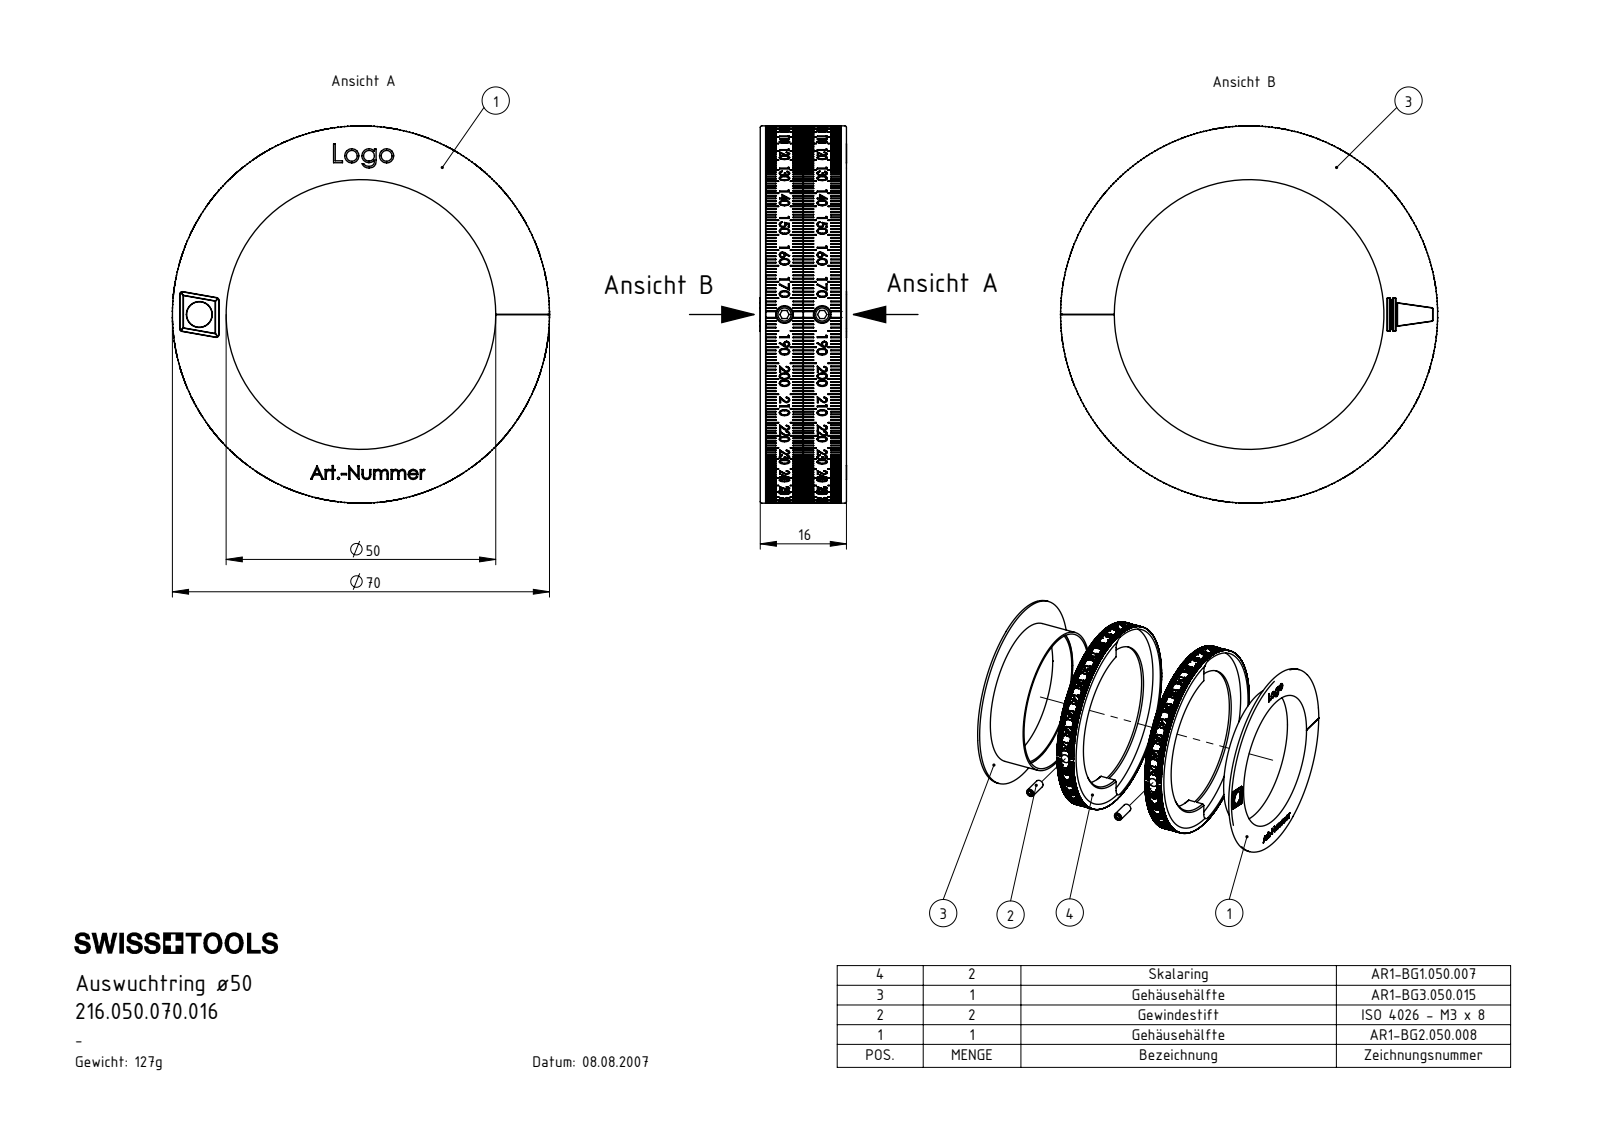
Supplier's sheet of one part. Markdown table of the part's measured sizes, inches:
| quantity | value |
| --- | --- |
| part name | AR1.U50.001.016; AR1-BG3.050.015_A_vereinfachte ansicht; AR1-BG1.050.007_A_vereinfachte ansicht; ISO 4026 - M4 x 8 (+1 more) |
| STEP written by | SolidWorks 2017 (AUTOMOTIVE_DESIGN) |
| units | inches |
| bodies | 6 solids, 86 faces (45 planar, 27 cylindrical, 14 other) |
| overall size | 2.756 × 2.756 × 0.63 |
| volume | 1.267 in³ |
| surface area | 42.74 in² |
| round holes (diameter × count) | 0.13 × 2, 1.97 × 1, 2.028 × 1, 2.087 × 1 |
| round bosses / shafts (diameter × count) | 0.118 × 2, 2.756 × 1 |
| partial cylindrical surfaces (radius × count) | 0.118 × 2, 1.339 × 1 |
| main face-to-face distances | 0.276, 0.039, 0.591, 0.122, 0.154, 0.272, 0.118, 0.15, 0.551, 0.63 |
| hole center spacings | 0.276 |
